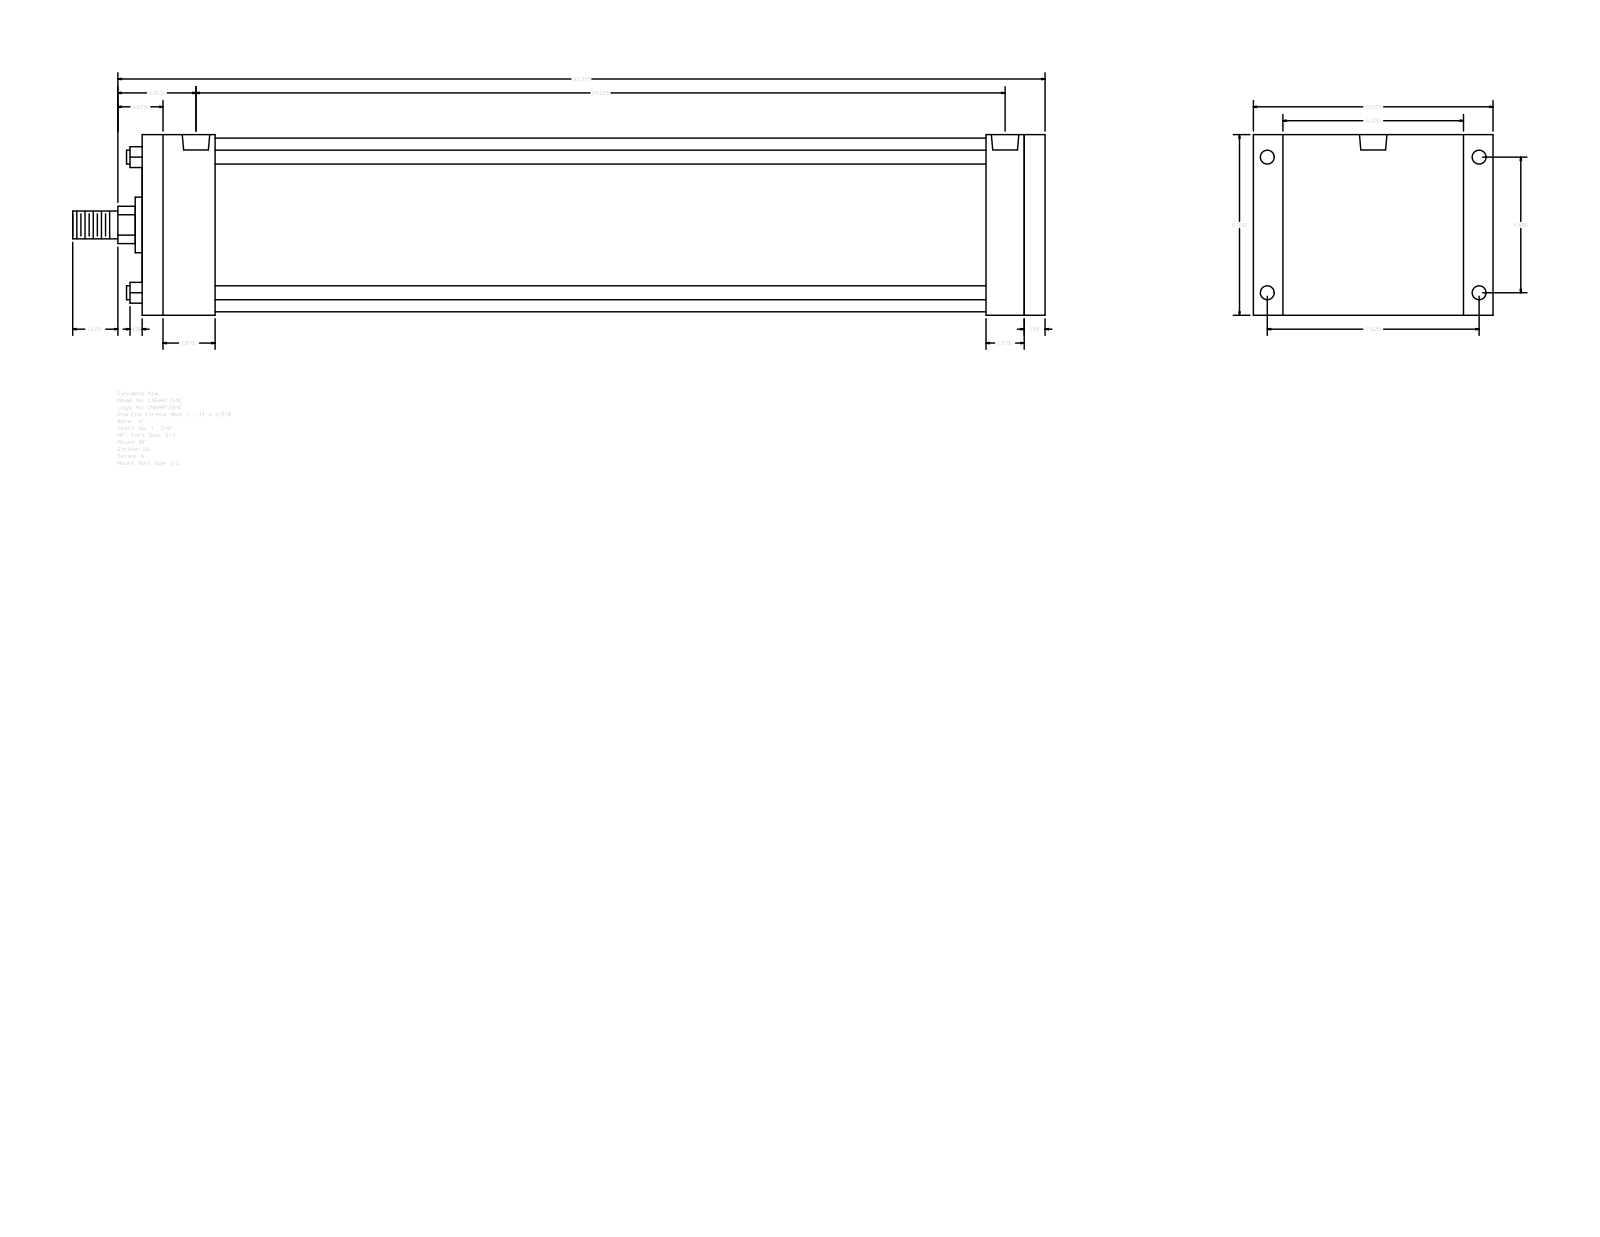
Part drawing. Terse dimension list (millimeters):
name: A_RF__0600_1.375
written by: GSSL Pune (CONFIG_CONTROL_DESIGN)
unit: mm
bodies: 0 solids, 92 faces (64 planar, 28 cylindrical, 0 other)
size: 889 × 219.07 × 165.1
holes: 4× ⌀12.7, 4× ⌀15.08, 2× ⌀25.12
bosses: 4× ⌀12.7, 1× ⌀158.75, 1× ⌀50.8, 1× ⌀34.92, 1× ⌀25.4
rounds: 1× R17.06
face distances: 165.1, 825.5, 806.44, 19.06, 66.67, 739.77, 758.83, 771.52, 704.85, 34.92
hole spacings: 5.56, 123.96, 193.68, 229.95, 728.65, 734.21, 739.77
